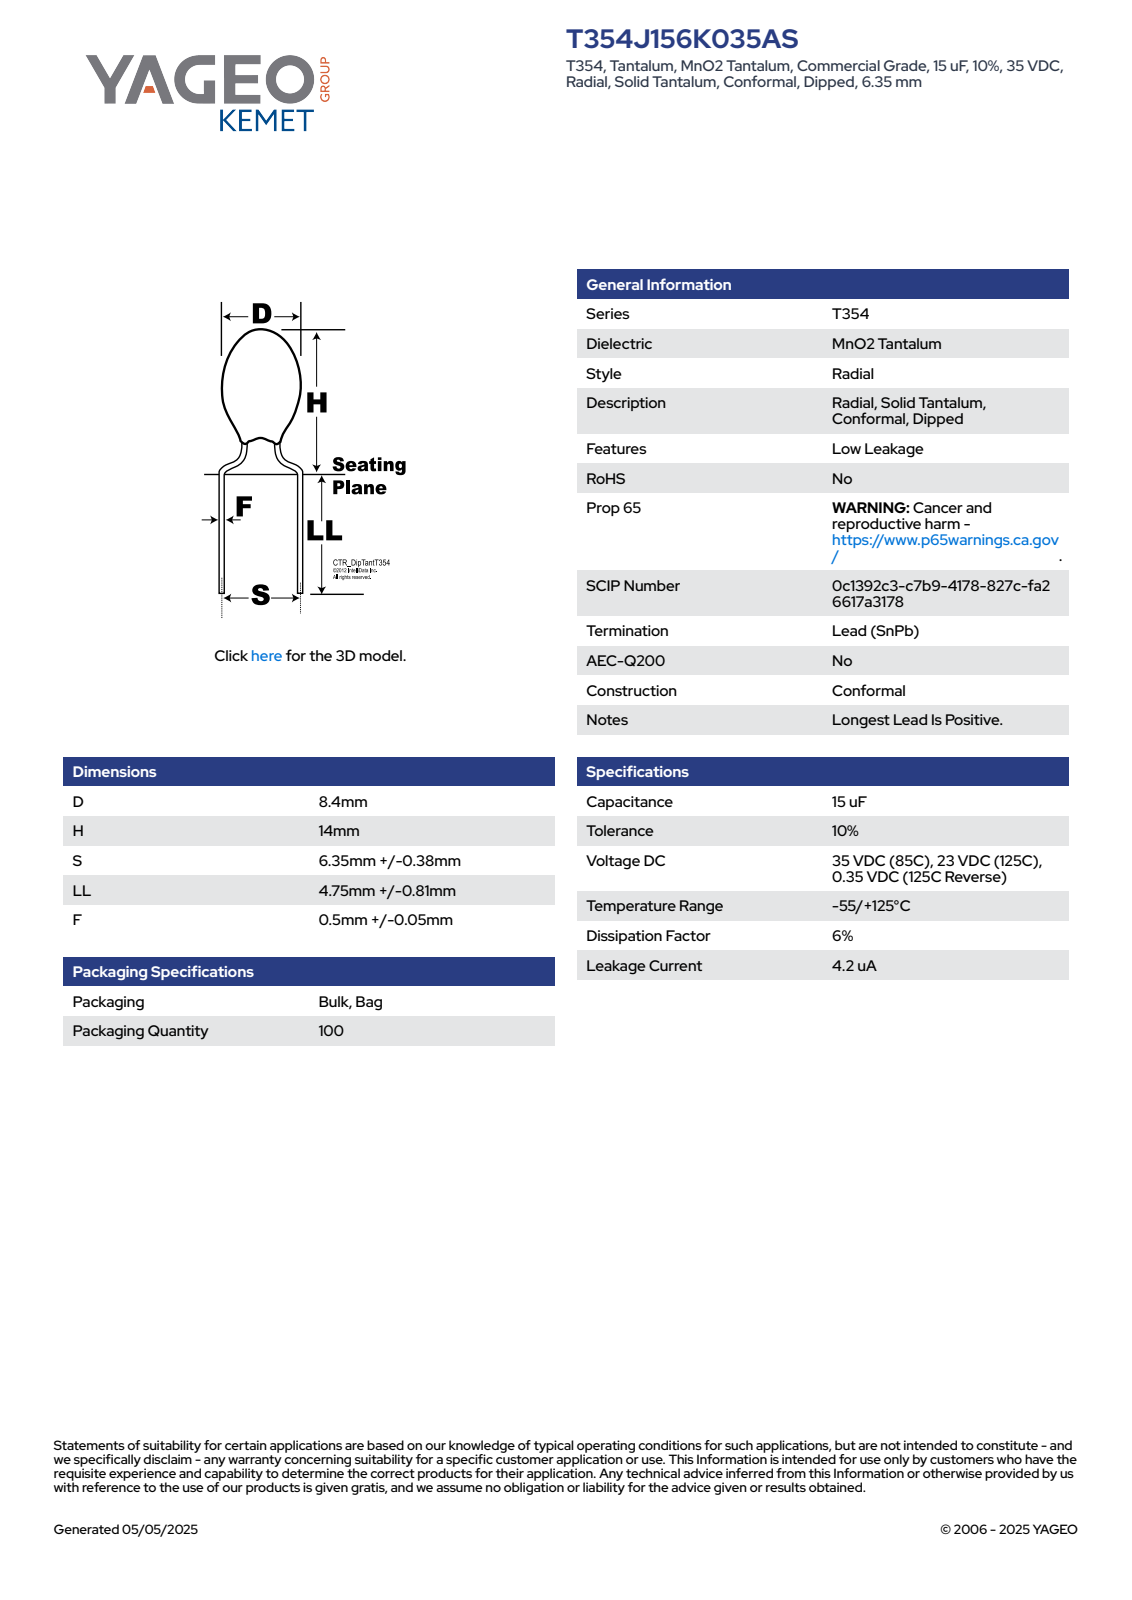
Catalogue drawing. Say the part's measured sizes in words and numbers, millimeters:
The part is named "CTR_T354_D8.4H14S6.35LL5.56F0.55". Its 3-D file was written by "SolidWorks 2014 (AUTOMOTIVE_DESIGN)". It is 1 solid with 81 faces: 26 planar, 10 cylindrical and 45 other. Overall it measures 19.56 by 8.4 by 8.4 millimeters. Its volume is 468 cubic millimeters and its surface area 335 square millimeters. Round bosses or shafts: 2 of diameter 0.55, 1 of diameter 8.4. Partial cylindrical surfaces (rounded edges, fillets, slot ends): 1 of radius 4.19. The main face-to-face distances are 9.77, 9.79, 19.56, 16.1, 6.31, 3.46, 15.1, 5.31, 1, 4.46.
